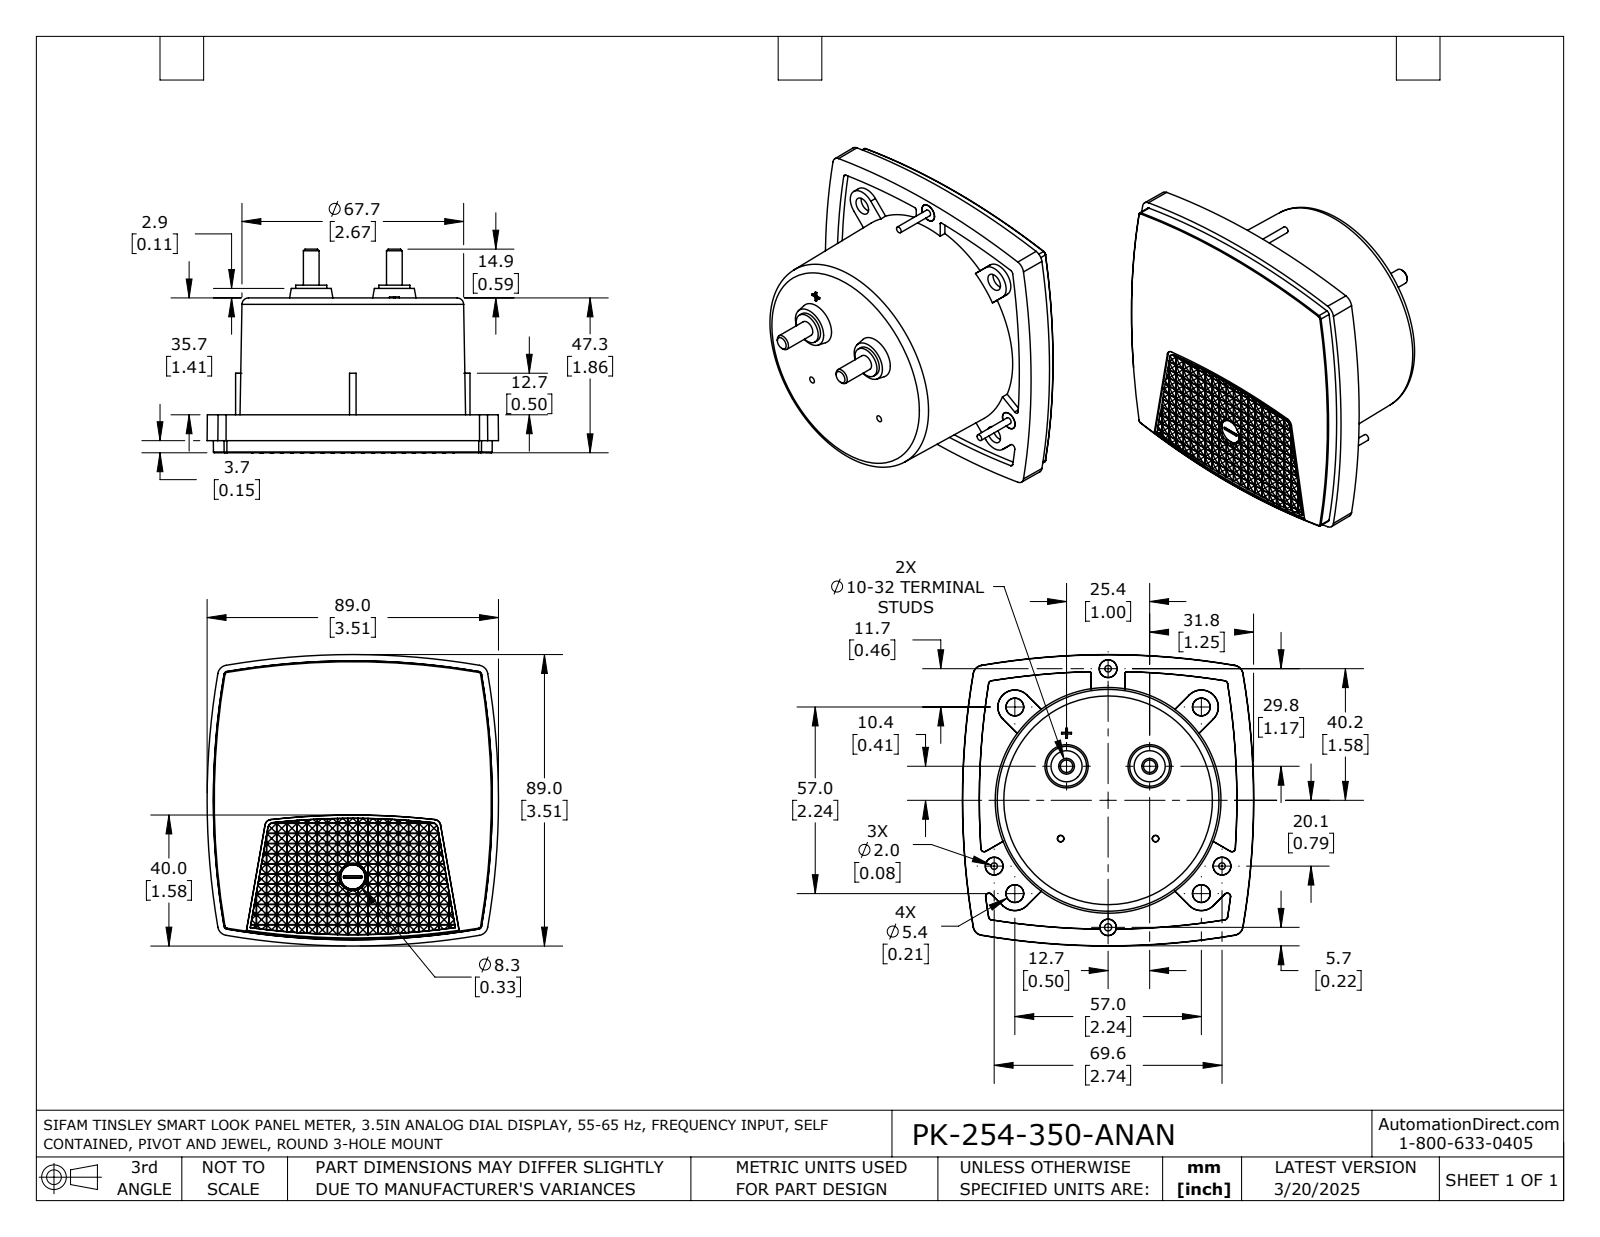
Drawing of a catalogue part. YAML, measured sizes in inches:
part_name: "PK-254-350-ANAN"
step_written_by: "SolidWorks 2021 (AUTOMOTIVE_DESIGN)"
units: inches
bodies: {solids: 1, faces: 1078, planar: 950, cylindrical: 23, other: 105}
overall_size: [3.505, 3.505, 2.453]
volume: 12.99
surface_area: 44.29
round_holes:
  - {diameter: 0.087, count: 1}
round_bosses_or_shafts:
  - {diameter: 0.213, count: 3}
  - {diameter: 0.079, count: 3}
  - {diameter: 0.374, count: 2}
  - {diameter: 0.189, count: 2}
partial_cylinders:
  - {radius: 8.961, count: 1}
face_to_face_distances: [1.862, 1.406, 0.457, 0.079, 1.484, 0.378, 0.024, 0.096, 0.072, 0.12]
